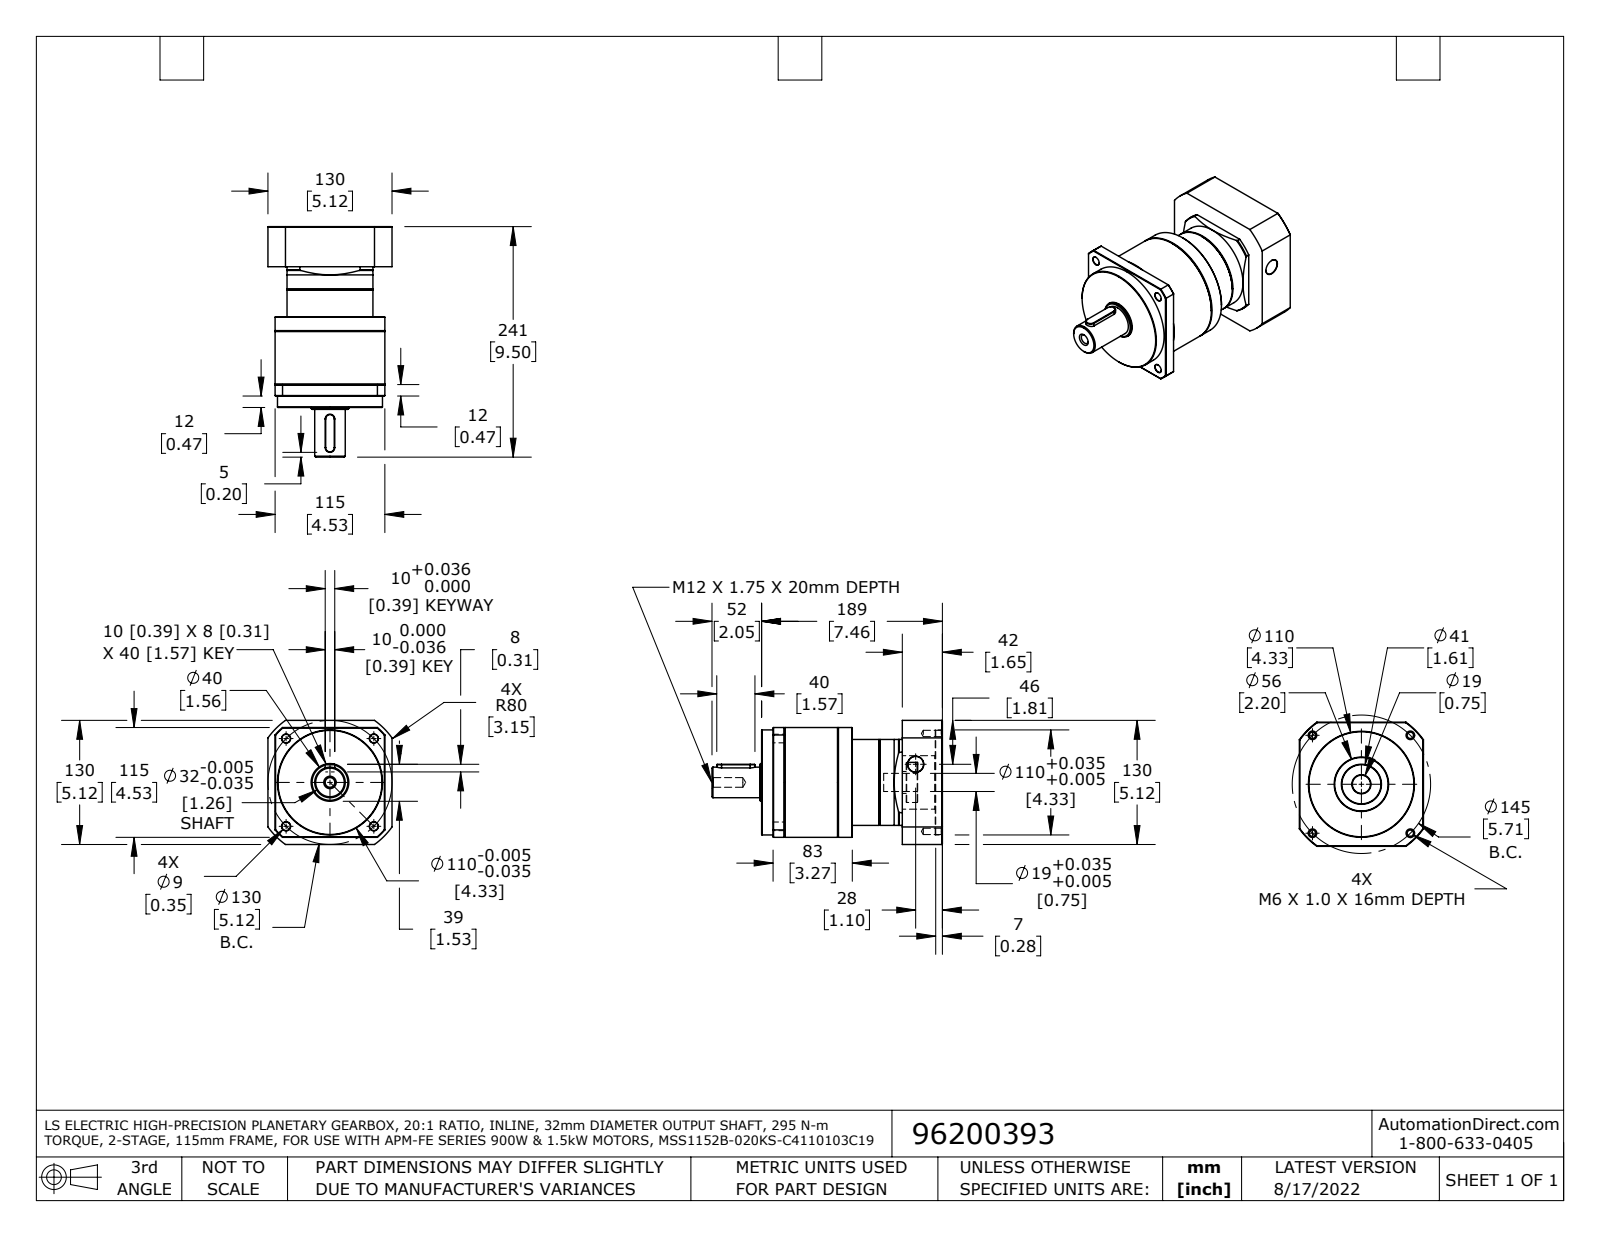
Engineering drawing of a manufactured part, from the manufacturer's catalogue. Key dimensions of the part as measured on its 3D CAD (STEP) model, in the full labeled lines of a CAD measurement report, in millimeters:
Part name (STEP PRODUCT): MSS1152B-C4120103 nc coord fxt
STEP written by: SolidWorks 2021 (AUTOMOTIVE_DESIGN)
Units: millimetres
Bodies: 3 solids, 194 faces (47 planar, 58 cylindrical, 89 other)
Overall size (bounding box): 241.4 × 130 × 130
Volume: 1 912 000 mm³ · Surface area: 163 900 mm²
Round holes (diameter × count): ⌀6.7 ×4, ⌀9 ×4, ⌀10.1 ×1, ⌀16.5 ×1, ⌀19 ×1, ⌀56 ×1
Round bosses / shafts (diameter × count): ⌀115 ×1, ⌀110 ×1, ⌀90 ×1, ⌀42 ×1, ⌀39.5 ×1, ⌀32 ×1, ⌀23 ×1
Partial cylindrical surfaces — rounded edges, fillets, slot ends (radius × count): R5 ×2, R76 ×1, R80 ×1
Main face-to-face distances: 23.9, 7.5, 147.4, 123.5, 130, 34.5, 58.4, 181.9, 12, 42
Hole centre spacings: 97.4, 7.5, 65, 102.5, 137.5, 72.5, 91.9, 91.9
